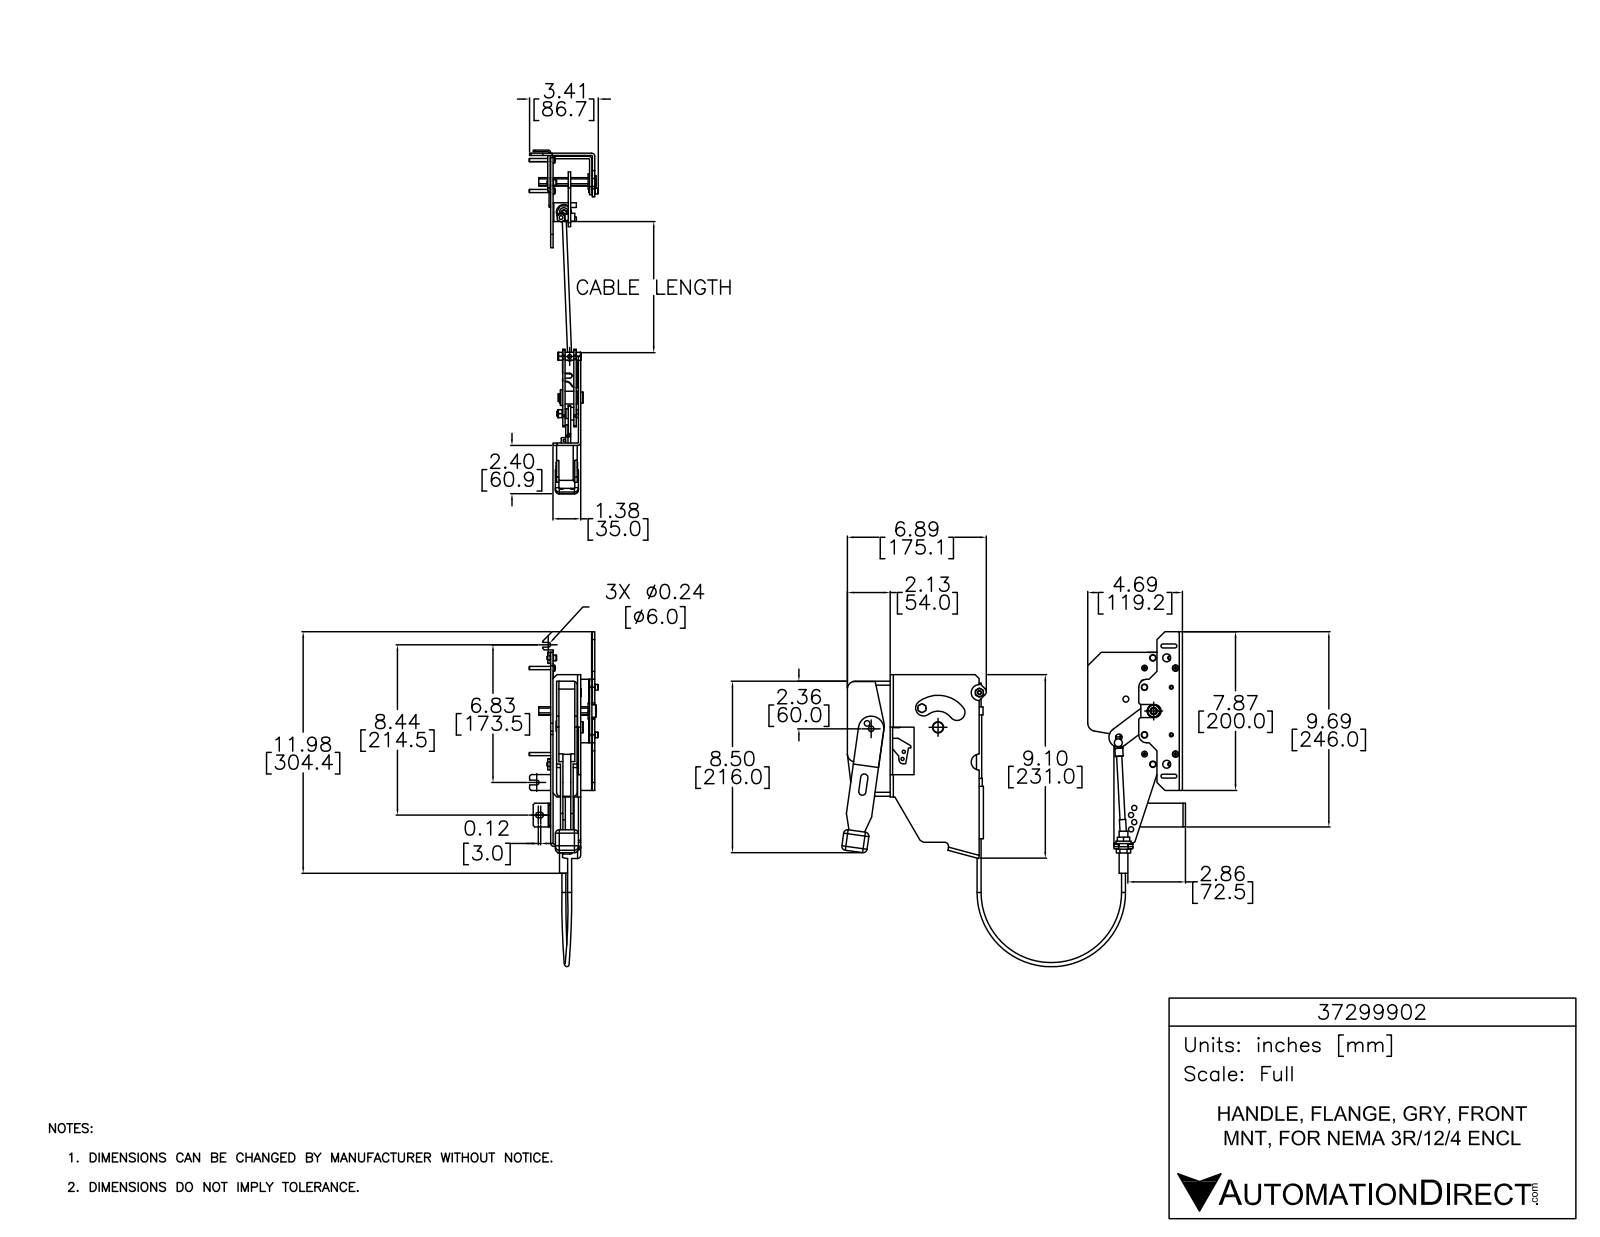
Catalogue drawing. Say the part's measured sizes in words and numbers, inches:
The part is named "37299002". Its 3-D file was written by "SolidWorks 2015 (AUTOMOTIVE_DESIGN)". It is 49 solids with 1007 faces: 467 planar, 432 cylindrical and 108 other. Overall it measures 17.044 by 16.614 by 3.429 inches. Its volume is 29.92 cubic inches and its surface area 414.3 square inches. Round holes: 18 of diameter 0.197, 4 of diameter 0.13, 4 of diameter 0.135, 4 of diameter 0.169, 4 of diameter 0.256, 2 of diameter 0.157, 2 of diameter 0.205, 2 of diameter 0.276, 2 of diameter 0.28, 2 of diameter 0.315, 2 of diameter 0.323, 2 of diameter 0.394. Round bosses or shafts: 9 of diameter 0.315, 6 of diameter 0.394, 4 of diameter 0.284, 4 of diameter 0.276, 4 of diameter 0.197, 4 of diameter 0.157, 4 of diameter 0.154, 2 of diameter 0.787. Partial cylindrical surfaces (rounded edges, fillets, slot ends): 24 of radius 0.197, 19 of radius 0.039, 11 of radius 0.394, 10 of radius 0.157, 6 of radius 0.012, 5 of radius 0.236, 4 of radius 0.008, 4 of radius 0.098. The main face-to-face distances are 0.118, 1.375, 1.493, 1.257, 2.071, 0.696, 0.197, 0.709, 14.378, 0.292. The hole center spacings are 0.15, 0.835, 5.276, 5.278, 5.341, 0.388, 0.569, 0.652.
